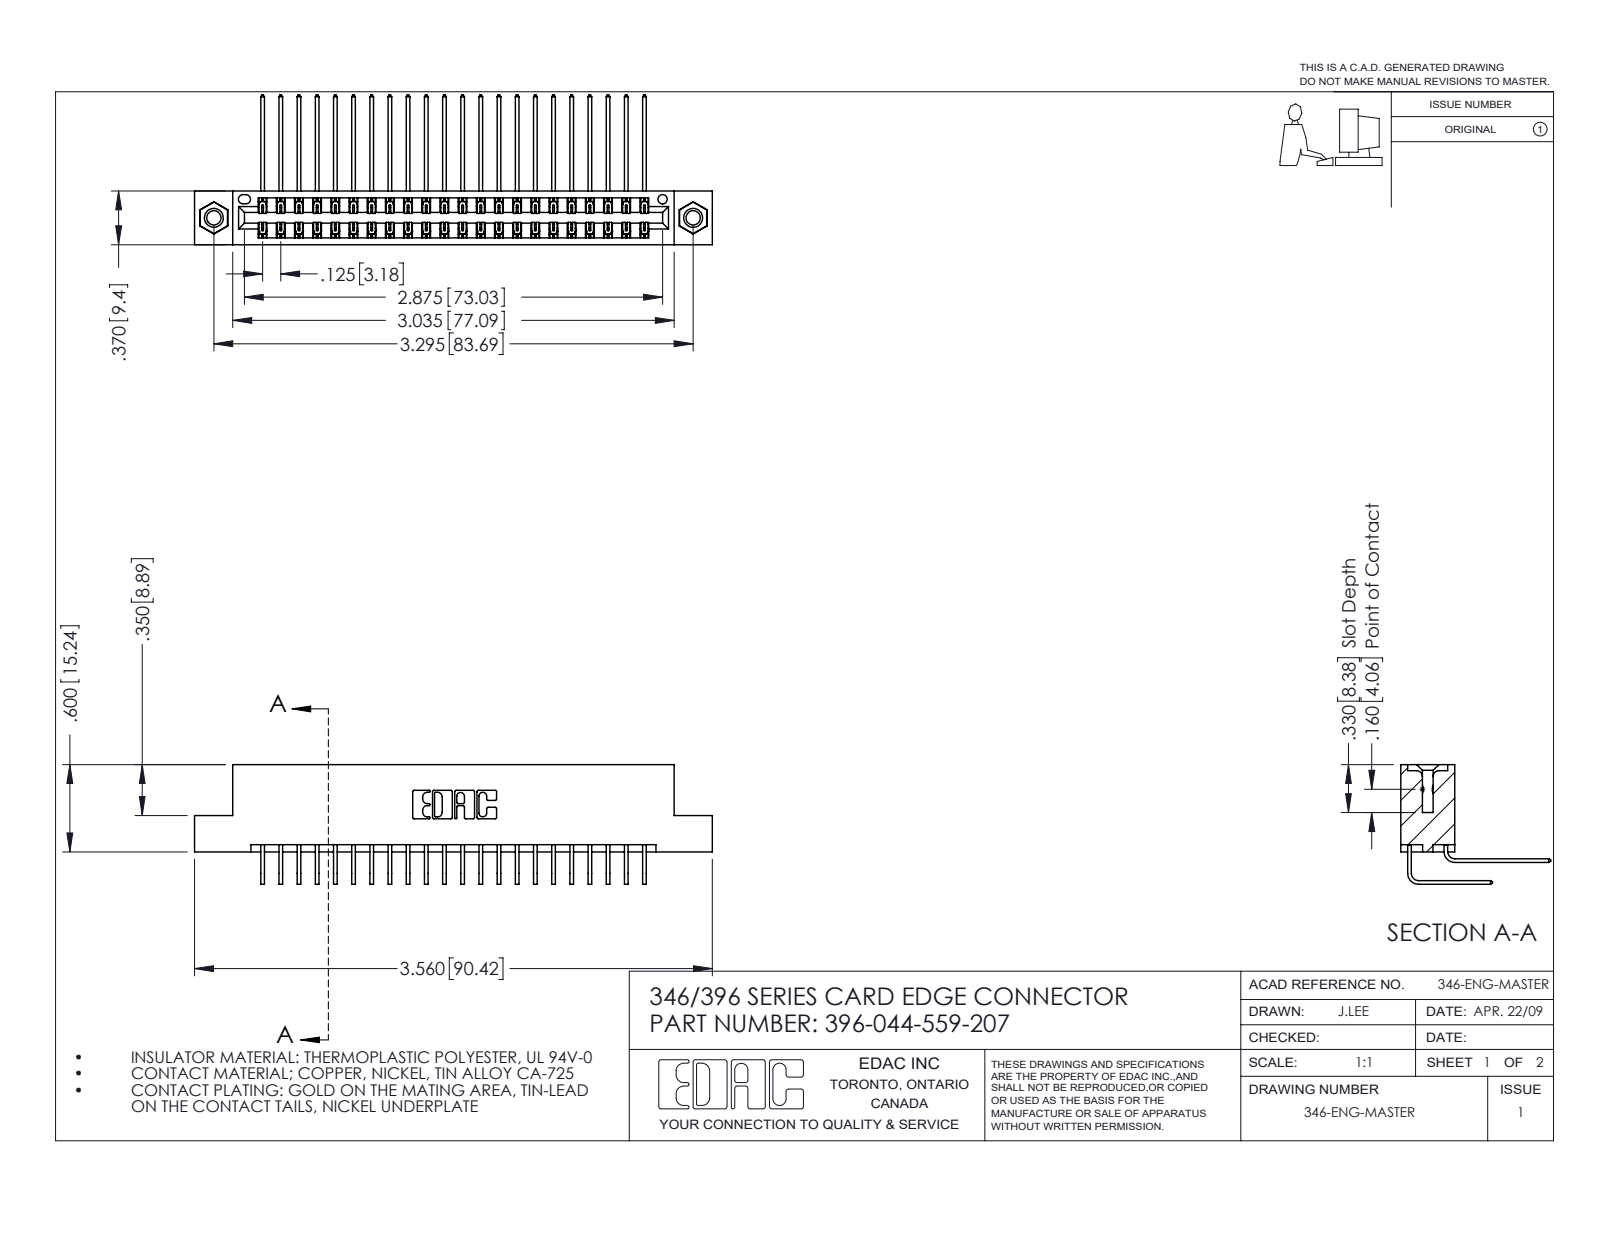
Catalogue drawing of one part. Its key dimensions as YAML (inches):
part_name: "396-044-559-207; 346 Part_Flush Mounting Lugs - 0.156 Dia-TI; 345-292-001_558 559 Tail - 1; 345-250-001_345-250-005-103 (+1 more)"
step_written_by: "SolidWorks 2016 (CONFIG_CONTROL_DESIGN)"
units: inches
bodies: {solids: 47, faces: 2558, planar: 1736, cylindrical: 806, other: 16}
overall_size: [3.56, 1.03, 0.823]
volume: 0.543
surface_area: 20.42
round_holes:
  - {diameter: 0.098, count: 2}
  - {diameter: 0.125, count: 2}
  - {diameter: 0.156, count: 2}
  - {diameter: 0.064, count: 1}
round_bosses_or_shafts:
  - {diameter: 0.155, count: 2}
partial_cylinders:
  - {radius: 0.006, count: 66}
  - {radius: 0.01, count: 22}
  - {radius: 0.007, count: 6}
  - {radius: 0.031, count: 6}
  - {radius: 0.026, count: 3}
  - {radius: 0.014, count: 2}
  - {radius: 0.022, count: 2}
  - {radius: 0.024, count: 2}
face_to_face_distances: [0.048, 0.322, 0.25, 0.025, 0.37, 0.072, 0.298, 0.275, 0.148, 0.222]
hole_center_spacings: [0.246, 3.087, 3.295]
